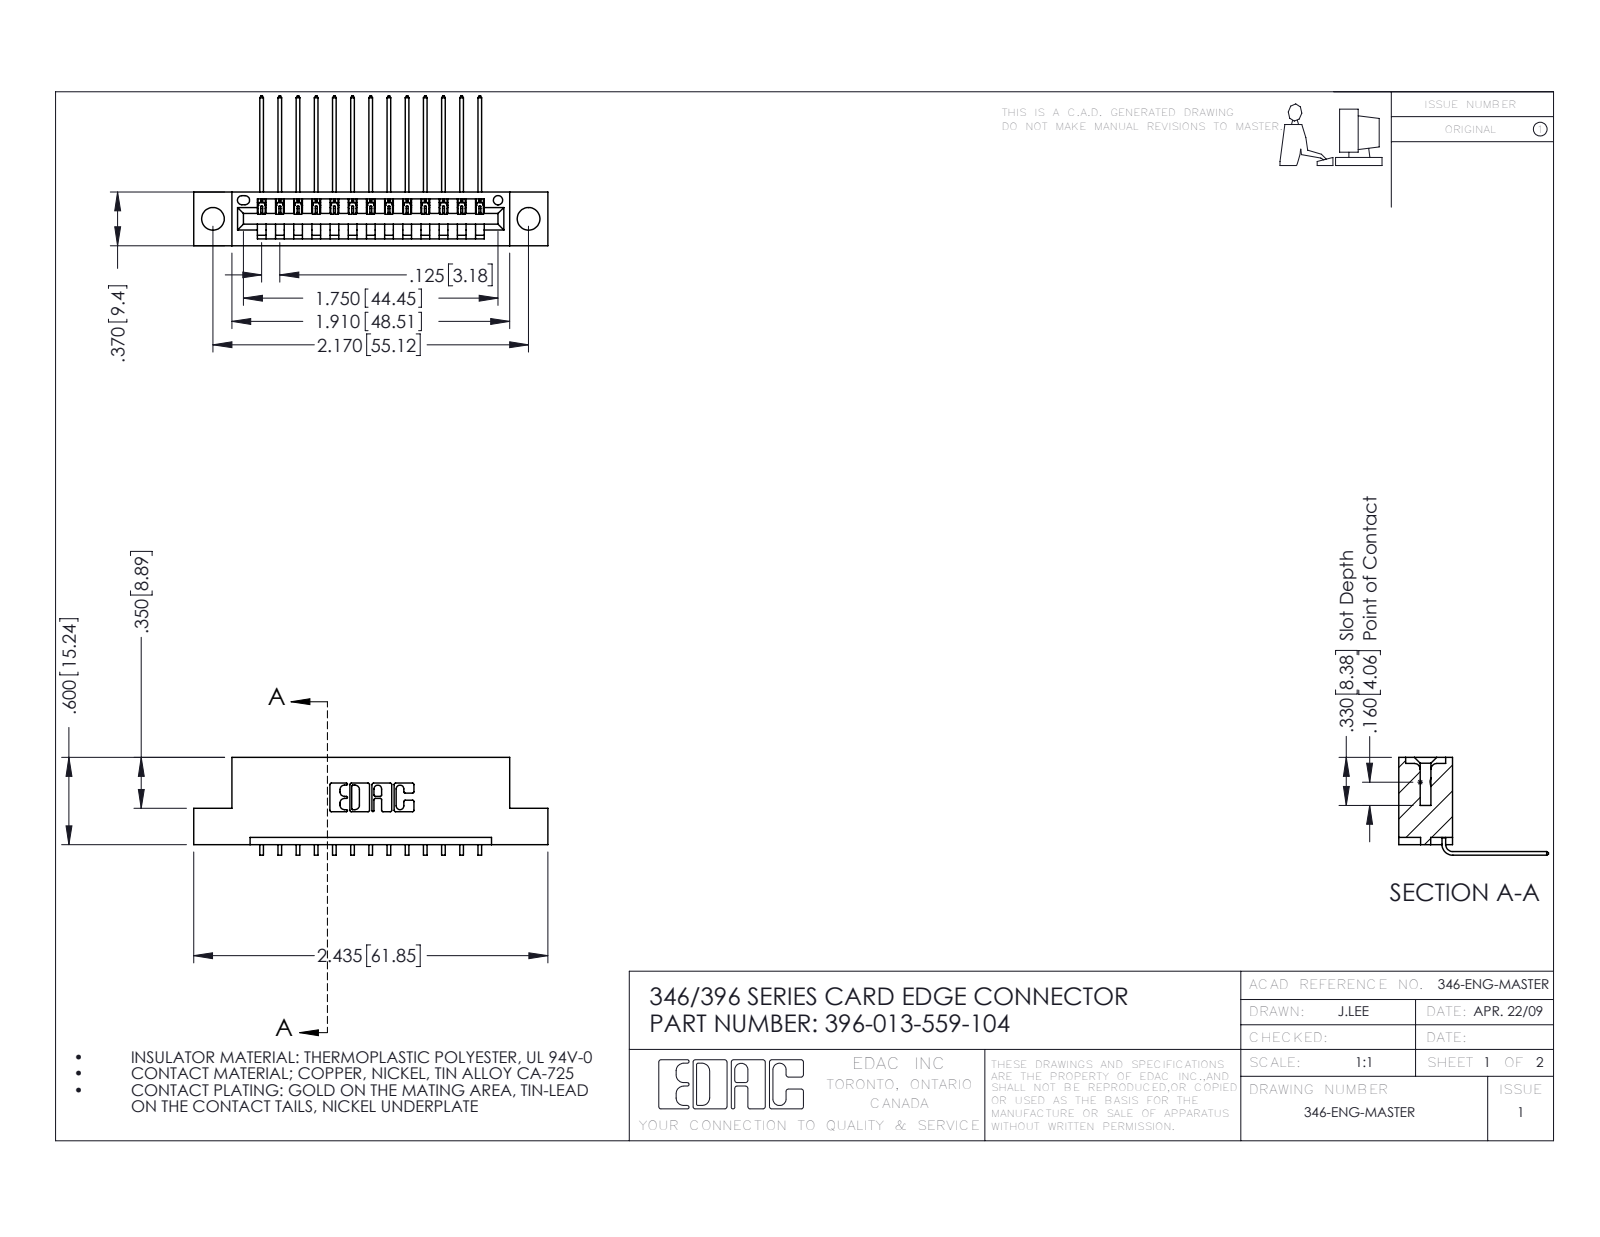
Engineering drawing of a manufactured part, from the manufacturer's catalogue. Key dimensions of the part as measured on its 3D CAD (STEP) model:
Part name (STEP PRODUCT): 396-013-559-104; 346 Part_Flush Mounting Lugs - 0.156 Dia-TH; 345-292-001_558 559 Tail - 1
STEP written by: SolidWorks 2016 (CONFIG_CONTROL_DESIGN)
Units: inches
Bodies: 14 solids, 902 faces (622 planar, 280 cylindrical, 0 other)
Overall size (bounding box): 2.435 × 1.03 × 0.673
Volume: 0.346 in³ · Surface area: 10.61 in²
Round holes (diameter × count): ⌀0.156 ×2, ⌀0.064 ×1
Partial cylindrical surfaces — rounded edges, fillets, slot ends (radius × count): R0.006 ×26, R0.01 ×22, R0.007 ×6, R0.031 ×6, R0.026 ×3, R0.031 ×2, R0.04 ×2, R0.014 ×1
Main face-to-face distances: 0.048, 0.25, 0.322, 0.37, 0.072, 0.025, 0.298, 0.148, 0.222, 0.1
Hole centre spacings: 0.246, 1.964, 2.17
